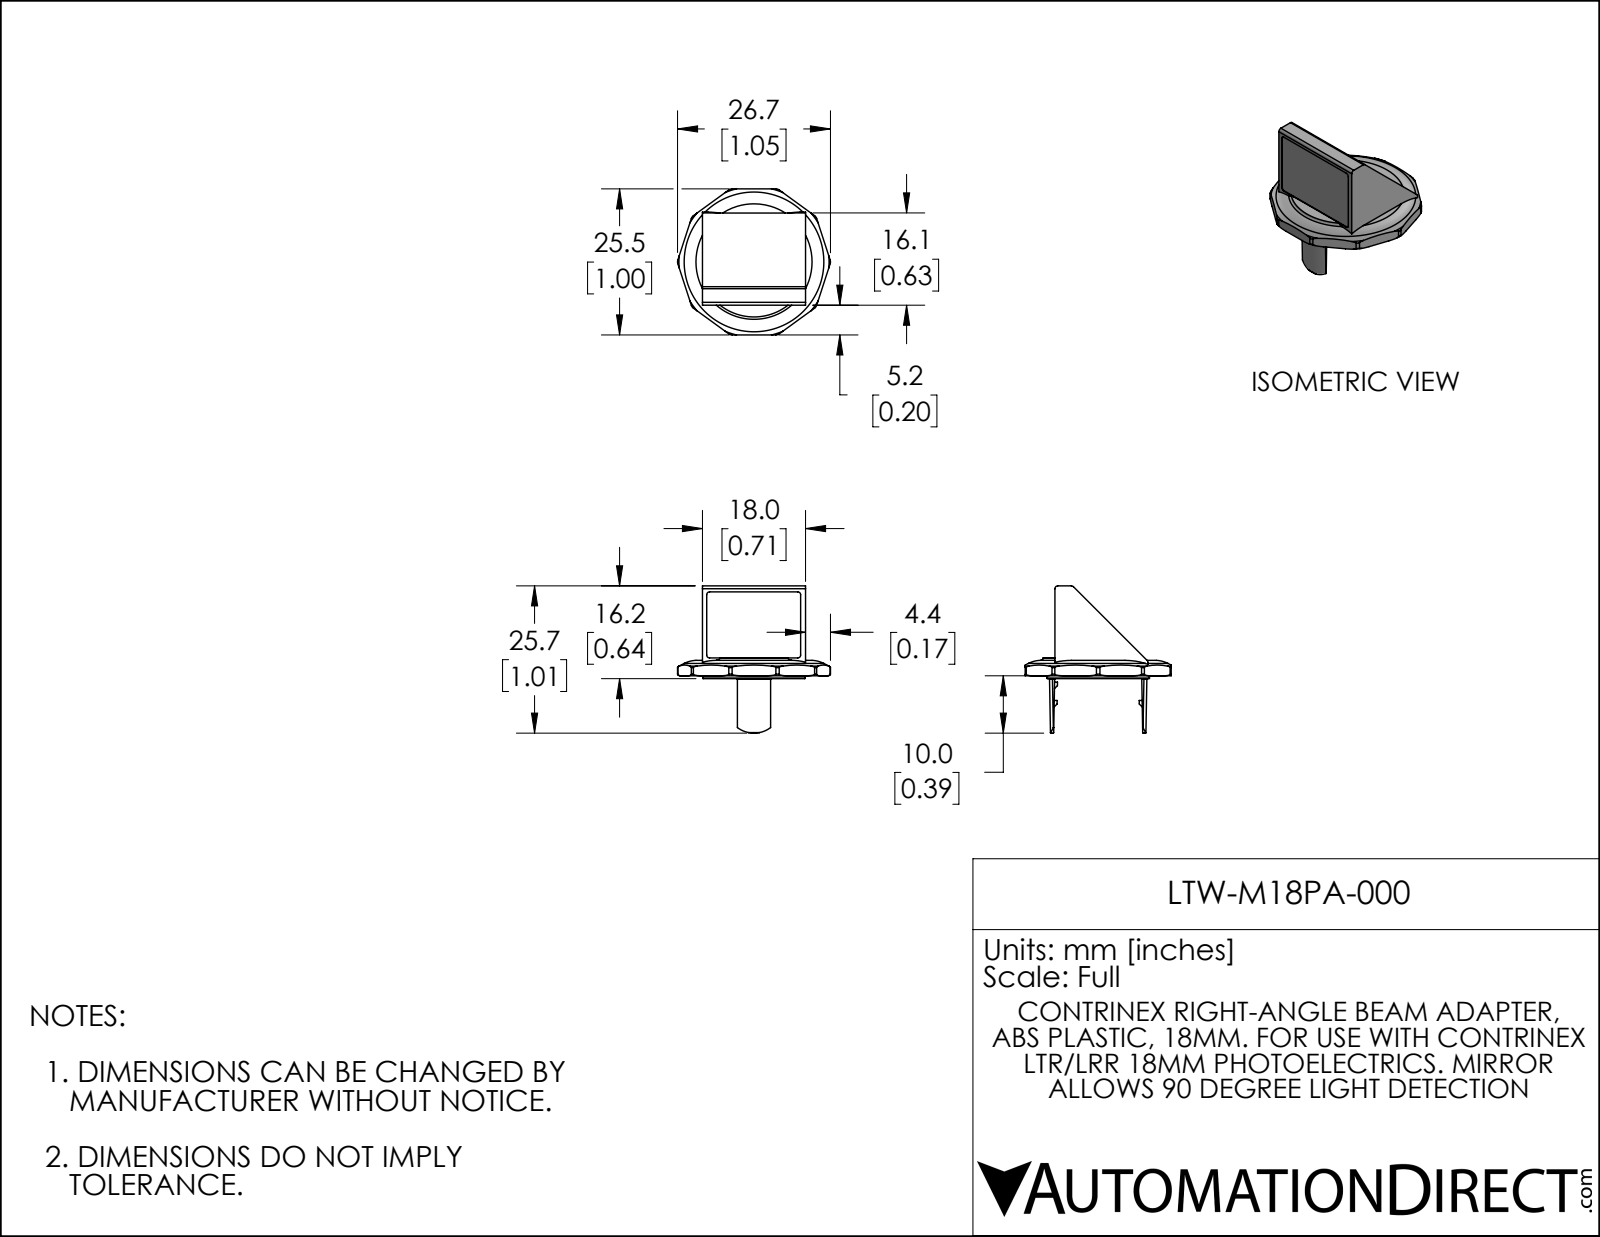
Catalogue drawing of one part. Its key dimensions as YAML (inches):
part_name: "LTW-M18PA-000"
step_written_by: "SolidWorks 2021 (AUTOMOTIVE_DESIGN)"
units: inches
bodies: {solids: 1, faces: 175, planar: 101, cylindrical: 32, other: 42}
overall_size: [1.051, 1.012, 1.004]
volume: 0.098
surface_area: 4.686
round_bosses_or_shafts:
  - {diameter: 0.984, count: 1}
  - {diameter: 0.705, count: 1}
partial_cylinders:
  - {radius: 0.039, count: 10}
  - {radius: 0.02, count: 7}
  - {radius: 0.004, count: 2}
  - {radius: 0.004, count: 2}
  - {radius: 0.189, count: 1}
  - {radius: 0.307, count: 1}
  - {radius: 0.329, count: 1}
face_to_face_distances: [0.022, 0.339, 0.369, 0.043, 0.666, 0.296, 0.326, 0.04, 0.709, 0.03]
